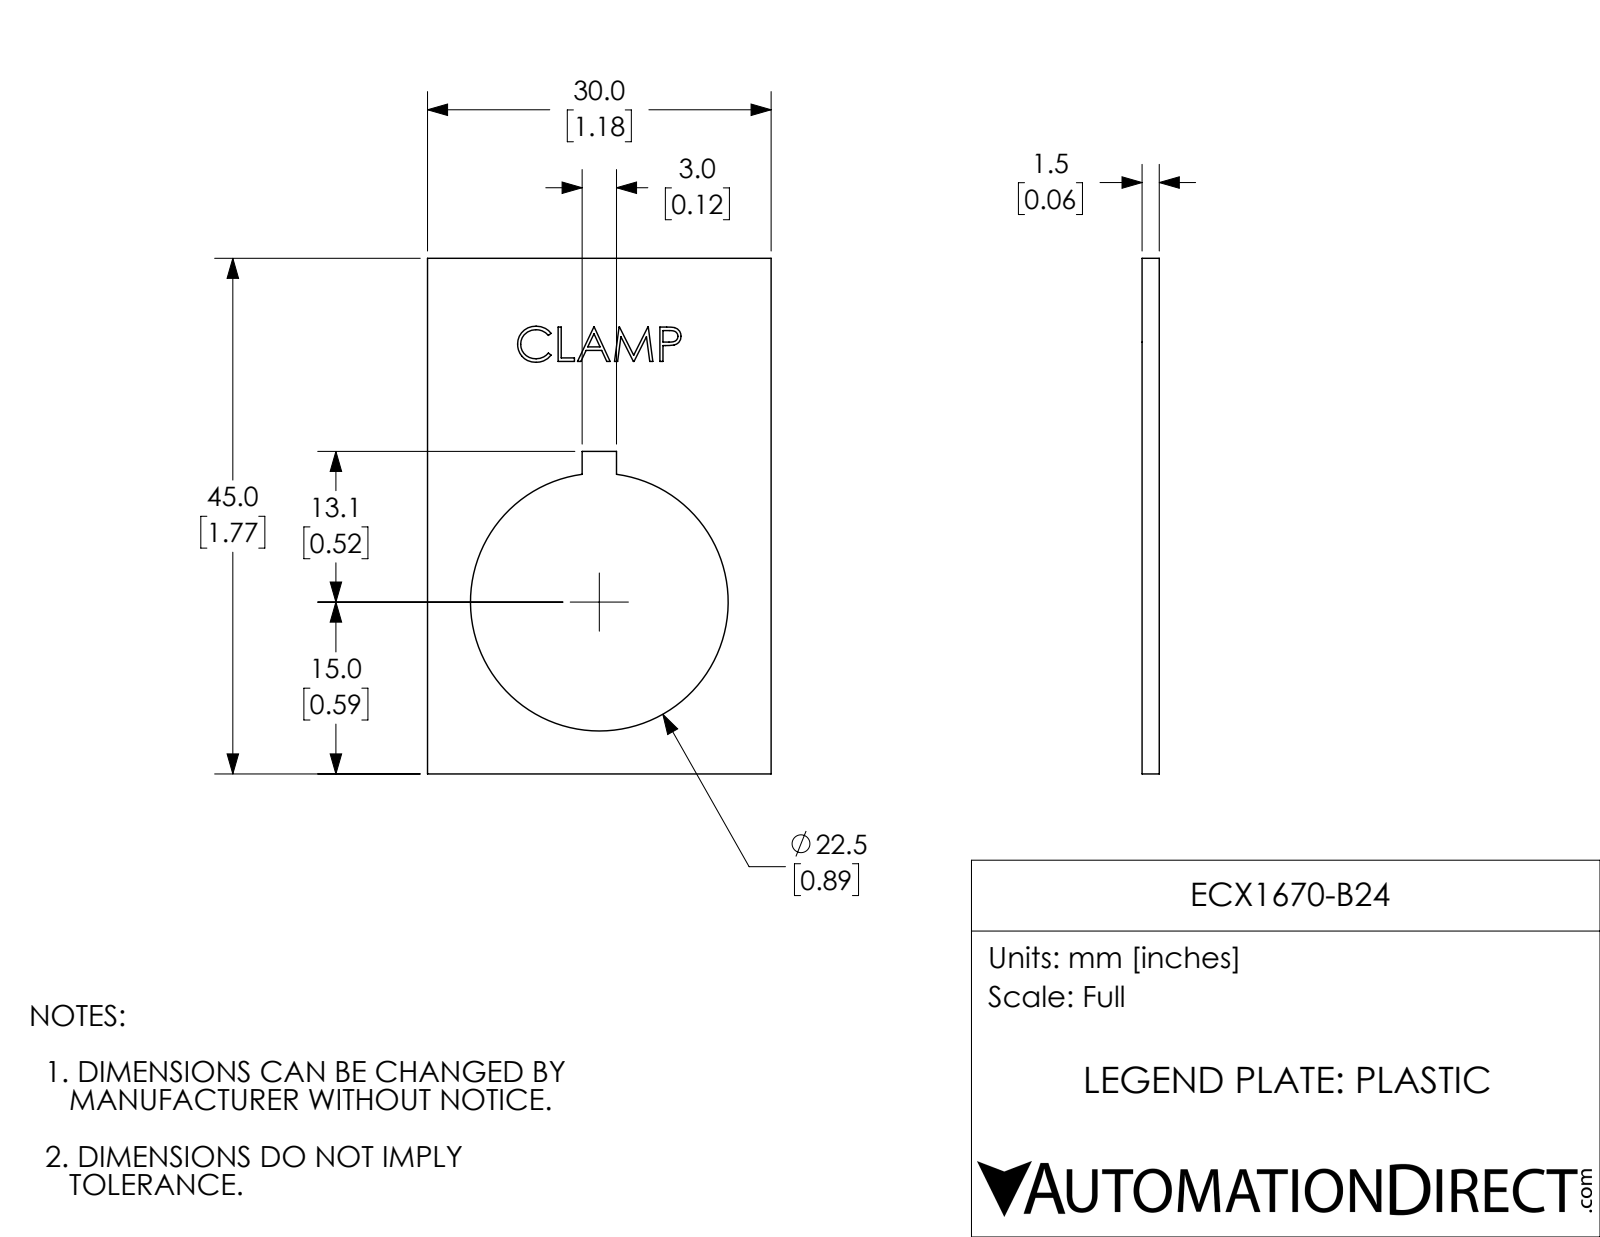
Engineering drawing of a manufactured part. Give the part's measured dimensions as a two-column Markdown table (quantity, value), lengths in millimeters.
| quantity | value |
| --- | --- |
| part name | ECX1670-B24 |
| STEP written by | SolidWorks 2017 (AUTOMOTIVE_DESIGN) |
| units | millimeters |
| bodies | 1 solid, 74 faces (56 planar, 3 cylindrical, 15 other) |
| overall size | 45 × 30 × 1.5 |
| volume | 1 400 mm³ |
| surface area | 2 232 mm² |
| round holes (diameter × count) | 22.5 × 1 |
| main face-to-face distances | 1.5, 30, 45, 1.5, 13.5, 16.5, 28.1, 16.8, 3, 8.9 |
